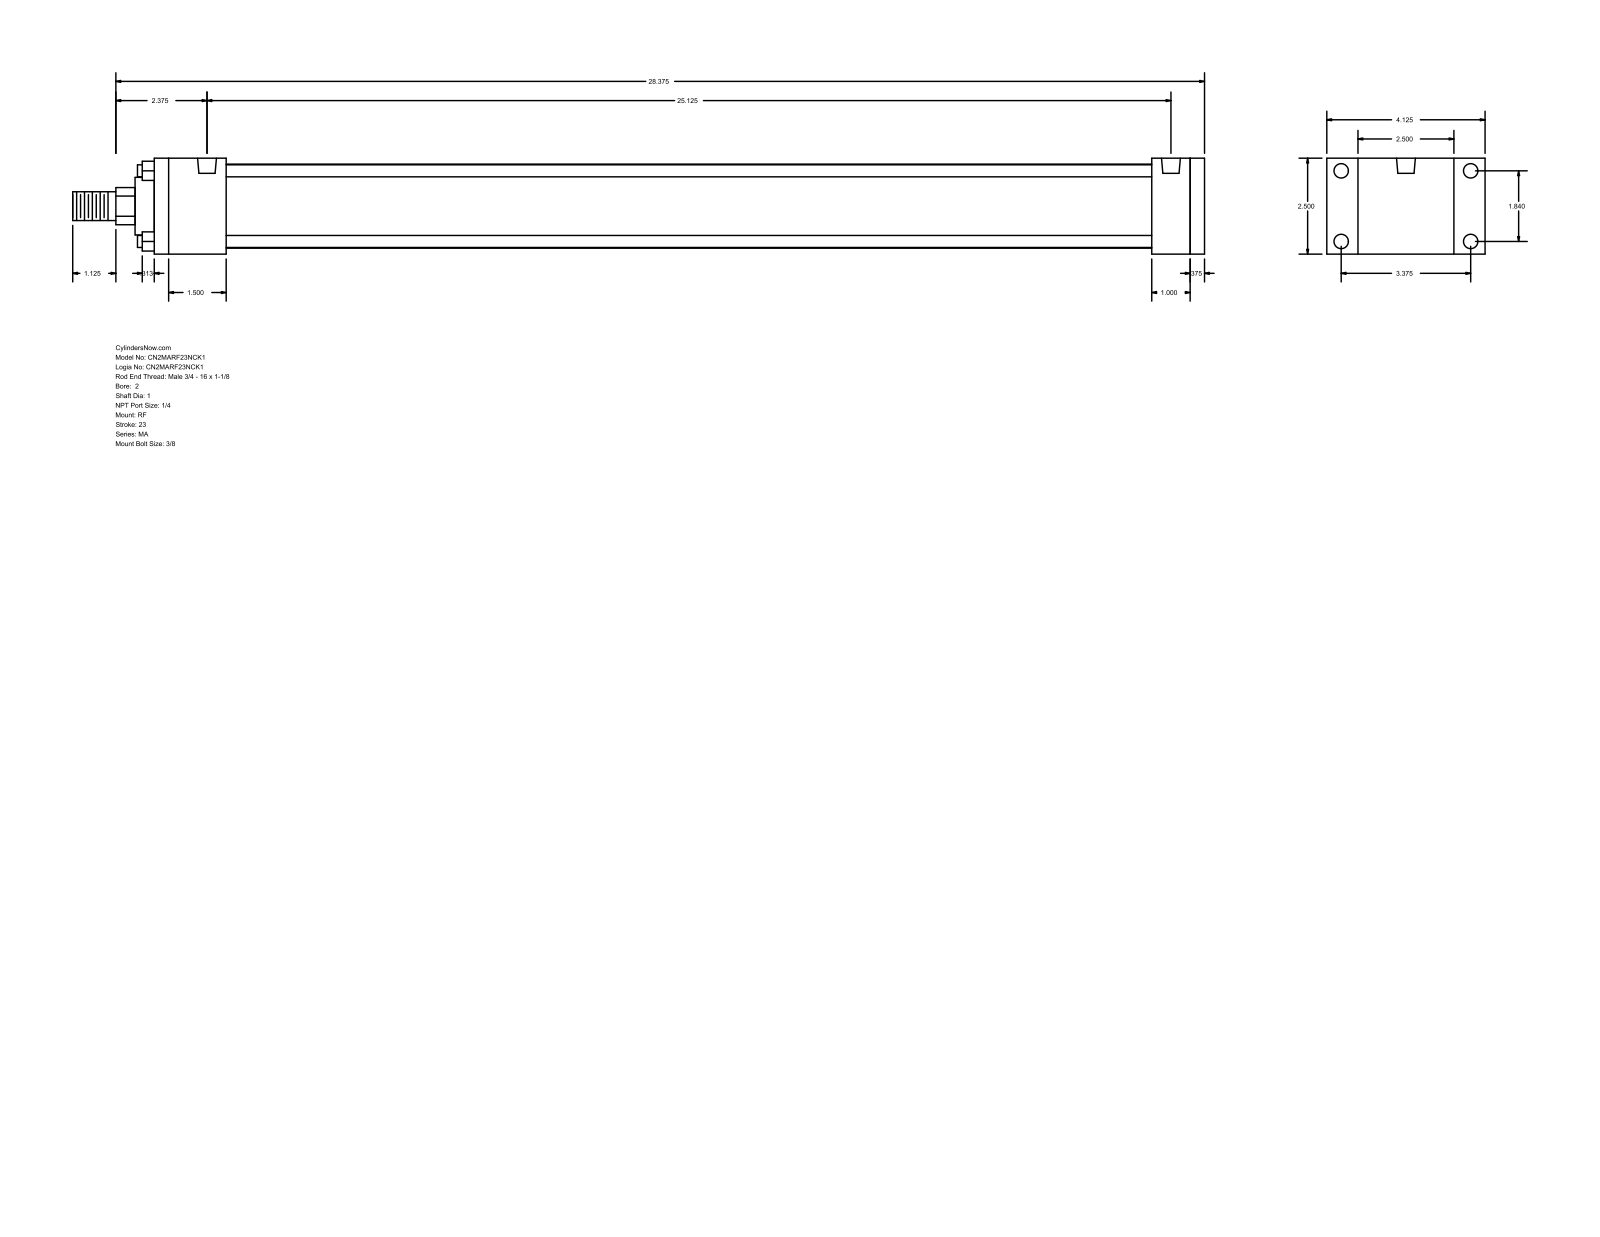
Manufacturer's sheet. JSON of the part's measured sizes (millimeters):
{"part_name": "MA_RF__0200_1", "step_written_by": "GSSL Pune (CONFIG_CONTROL_DESIGN)", "units": "millimeters", "bodies": {"solids": 0, "faces": 92, "planar": 64, "cylindrical": 28, "other": 0}, "overall_size": [749.3, 104.78, 63.5], "round_holes": [[7.94, 4], [9.53, 4], [12.49, 2]], "round_bosses_or_shafts": [[7.94, 4], [55.63, 1], [38.1, 1], [25.4, 1], [19.05, 1]], "partial_cylinders_radius": [[12.29, 1]], "face_to_face_distances": [63.5, 685.8, 9.53, 695.33, 25.4, 20.64, 12.7, 47.63, 638.17, 647.7], "hole_center_spacings": [46.74, 85.72, 97.63, 638.17]}
